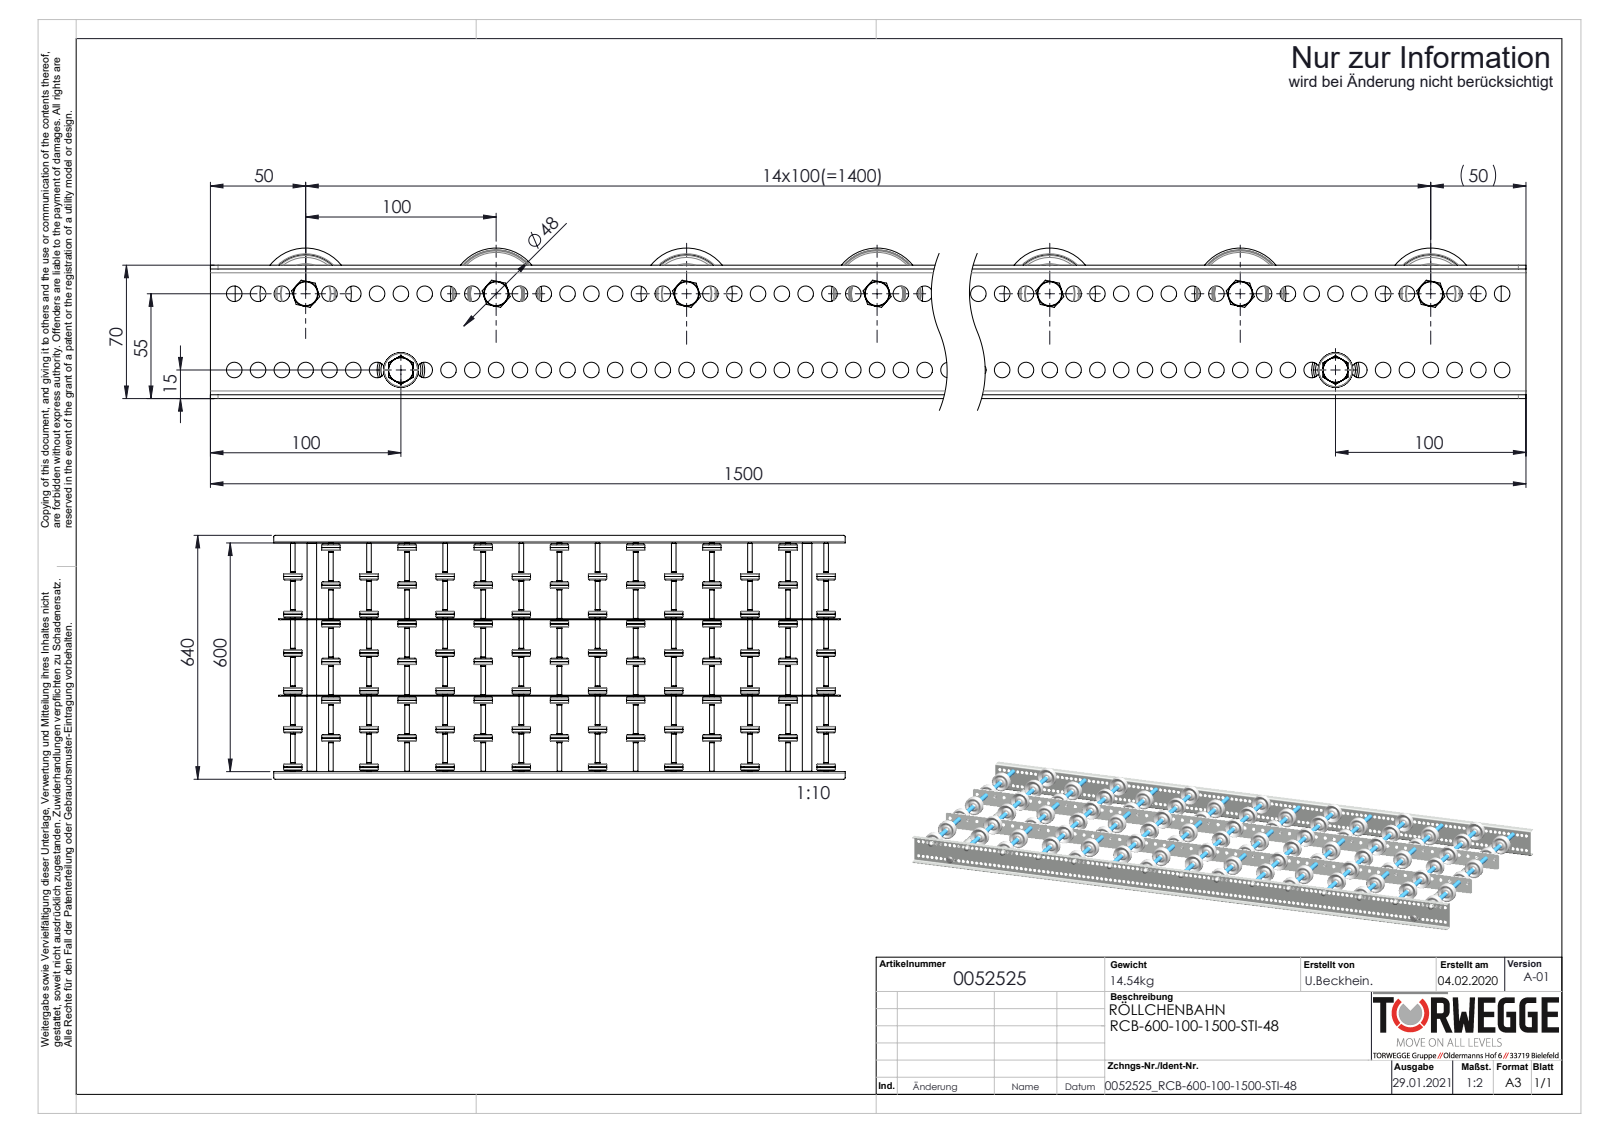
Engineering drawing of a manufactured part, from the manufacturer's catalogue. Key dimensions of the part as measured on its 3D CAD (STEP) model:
Part name (STEP PRODUCT): S100994_Sperrzahnschraube_M08x16-8.8-A2K; S100100_Längstraverse-42x2,5_S100102_Lngstraverse-RB-L1500; K0011528_2200-48-8; Hutmutter_DIN_1587_M8 (+6 more)
STEP written by: SolidWorks 2020 (AUTOMOTIVE_DESIGN)
Units: millimetres
Bodies: 329 solids, 10188 faces (2022 planar, 4102 cylindrical, 4064 other)
Overall size (bounding box): 1500 × 640 × 79
Volume: 3 718 000 mm³ · Surface area: 2 882 000 mm²
Round holes (diameter × count): ⌀8.2 ×238, ⌀8.5 ×59, ⌀6.65 ×15, ⌀8 ×15, ⌀9.65 ×15, ⌀15 ×15, ⌀41 ×15, ⌀6.8 ×2, ⌀21 ×2
Round bosses / shafts (diameter × count): ⌀48 ×15, ⌀13 ×15, ⌀12.5 ×15, ⌀12.4 ×15, ⌀12 ×15, ⌀11.5 ×15, ⌀25 ×2, ⌀8 ×2
Partial cylindrical surfaces — rounded edges, fillets, slot ends (radius × count): R4 ×8, R2 ×4, R5 ×4
Main face-to-face distances: 200.5, 2, 401, 602, 99, 76, 2.5, 198, 12, 111
Hole centre spacings: 12.5, 25, 37.5, 50, 62.5, 75, 87.5, 100
